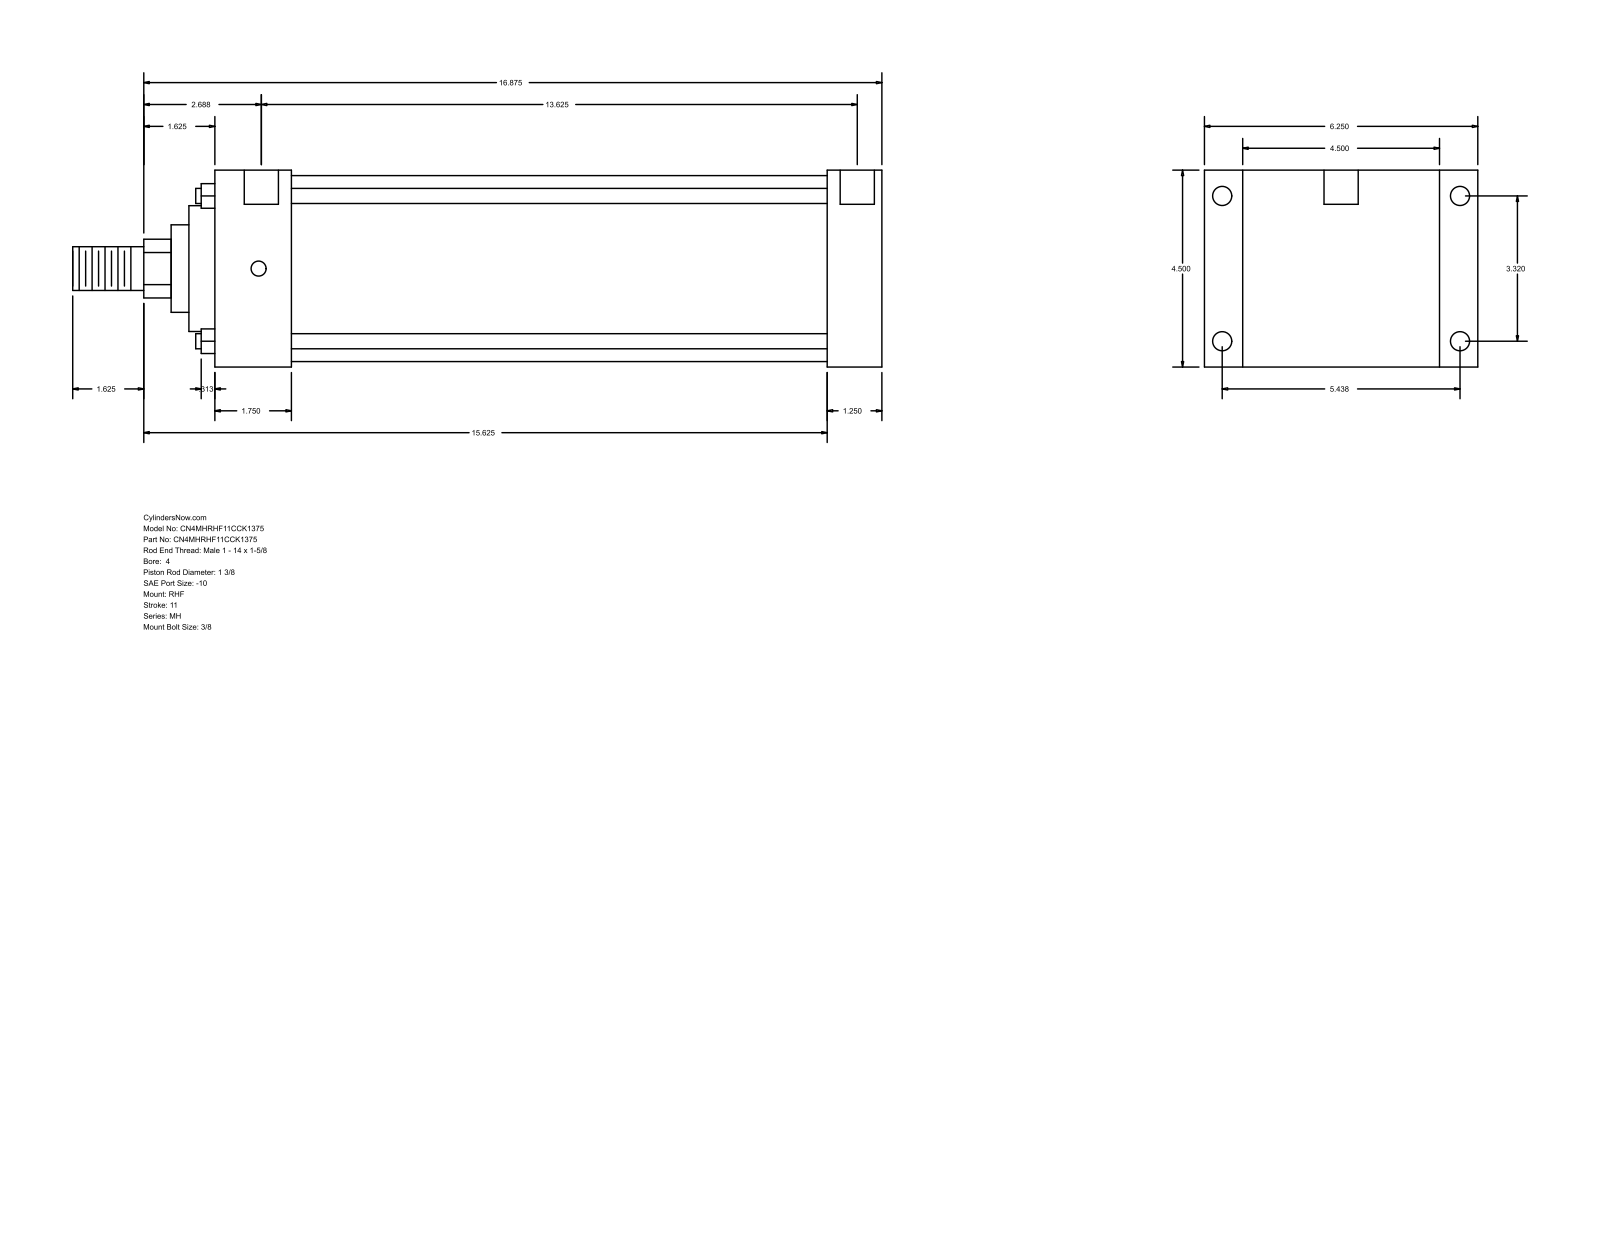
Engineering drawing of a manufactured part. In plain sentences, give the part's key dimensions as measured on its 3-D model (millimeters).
The part is named "MH_RHF__0400_1.375". Its 3-D file was written by "GSSL Pune (CONFIG_CONTROL_DESIGN)". It is 0 solids with 90 faces: 61 planar, 29 cylindrical and 0 other. Overall it measures 469.9 by 158.75 by 114.3 millimeters. Round holes: 4 of diameter 8.73, 4 of diameter 11.13, 2 of diameter 19.84. Round bosses or shafts: 4 of diameter 8.76, 1 of diameter 107.95, 1 of diameter 73.03, 1 of diameter 50.8, 1 of diameter 34.92, 1 of diameter 25.4. Partial cylindrical surfaces (rounded edges, fillets, slot ends): 1 of radius 17.06. The main face-to-face distances are 114.3, 31.74, 355.61, 387.35, 22.23, 136.53, 44.45, 311.16, 342.9, 158.76. The hole center spacings are 1.59, 84.32, 138.12, 161.82, 347.67, 349.26, 346.08.
